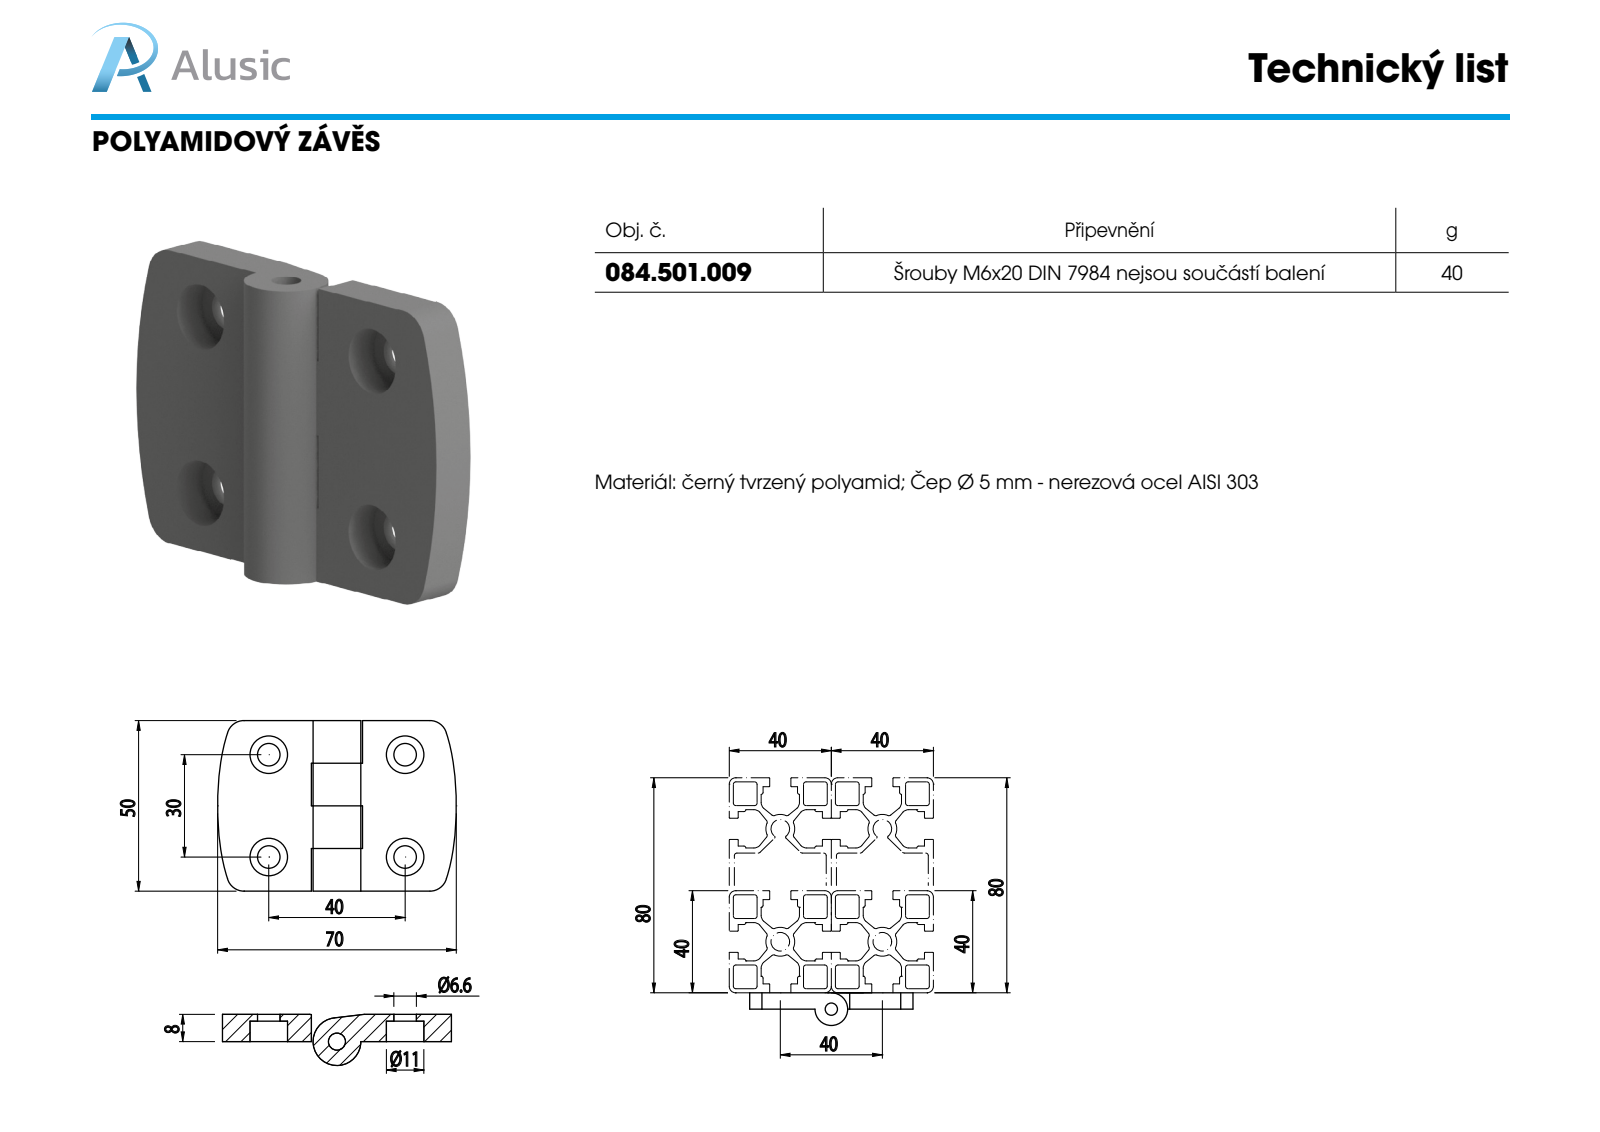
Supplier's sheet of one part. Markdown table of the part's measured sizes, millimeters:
| quantity | value |
| --- | --- |
| part name | 084.501.009 ALETTA; 084.501.009 |
| STEP written by | SolidWorks 2011 (CONFIG_CONTROL_DESIGN) |
| units | millimeters |
| bodies | 2 solids, 58 faces (24 planar, 34 cylindrical, 0 other) |
| overall size | 69.95 × 50 × 16.83 |
| volume | 25 904 mm³ |
| surface area | 11 920 mm² |
| round holes (diameter × count) | 6.6 × 4, 11 × 4, 5 × 1 |
| round bosses / shafts (diameter × count) | 14 × 1 |
| partial cylindrical surfaces (radius × count) | 5 × 4, 80 × 2 |
| main face-to-face distances | 12.5, 8, 8.01, 25, 37.5, 50, 6, 2, 2.01 |
| hole center spacings | 30 |
